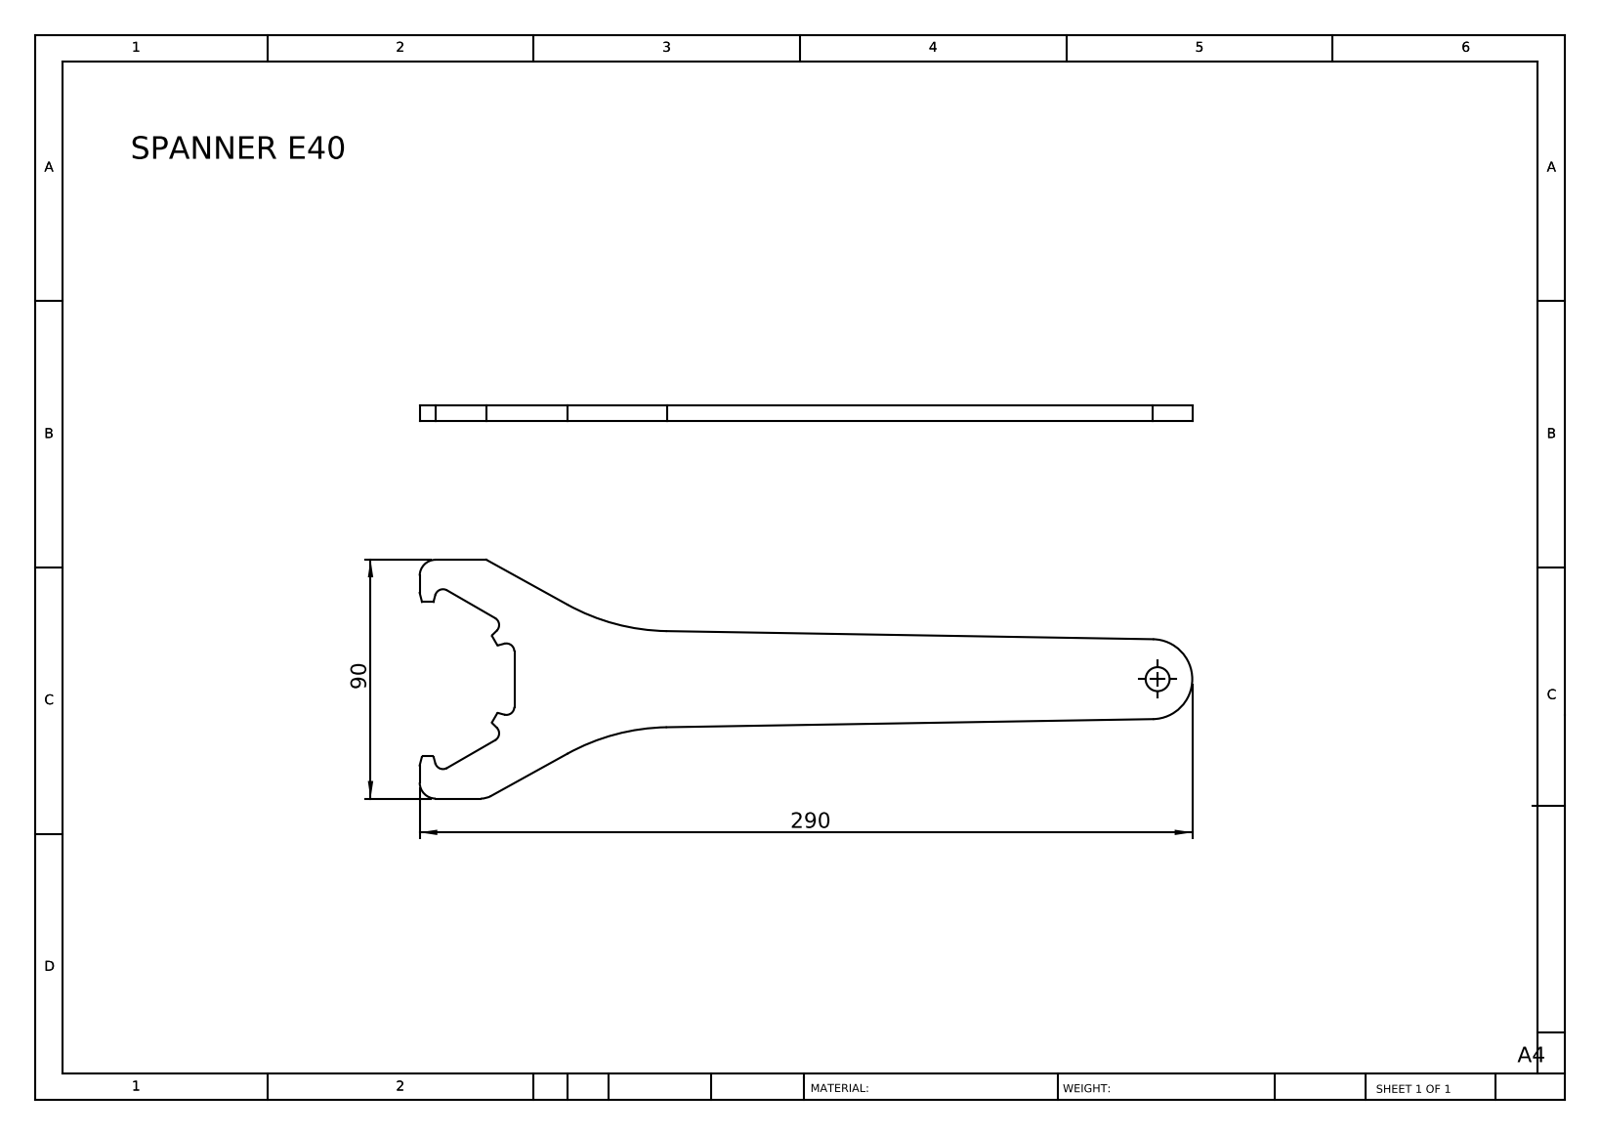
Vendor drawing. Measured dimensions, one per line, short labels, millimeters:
name: SPANNER E40
written by: SolidWorks 2014 (CONFIG_CONTROL_DESIGN)
unit: mm
bodies: 1 solid, 47 faces (25 planar, 22 cylindrical, 0 other)
size: 290 × 89.66 × 6
volume: 63 010 mm³; area: 25 756 mm²
holes: 1× ⌀9
rounds: 6× R0.4, 6× R3, 2× R6, 2× R80, 1× R8, 1× R15
face distances: 6, 89.66, 35.52, 15.83, 73.83, 58
